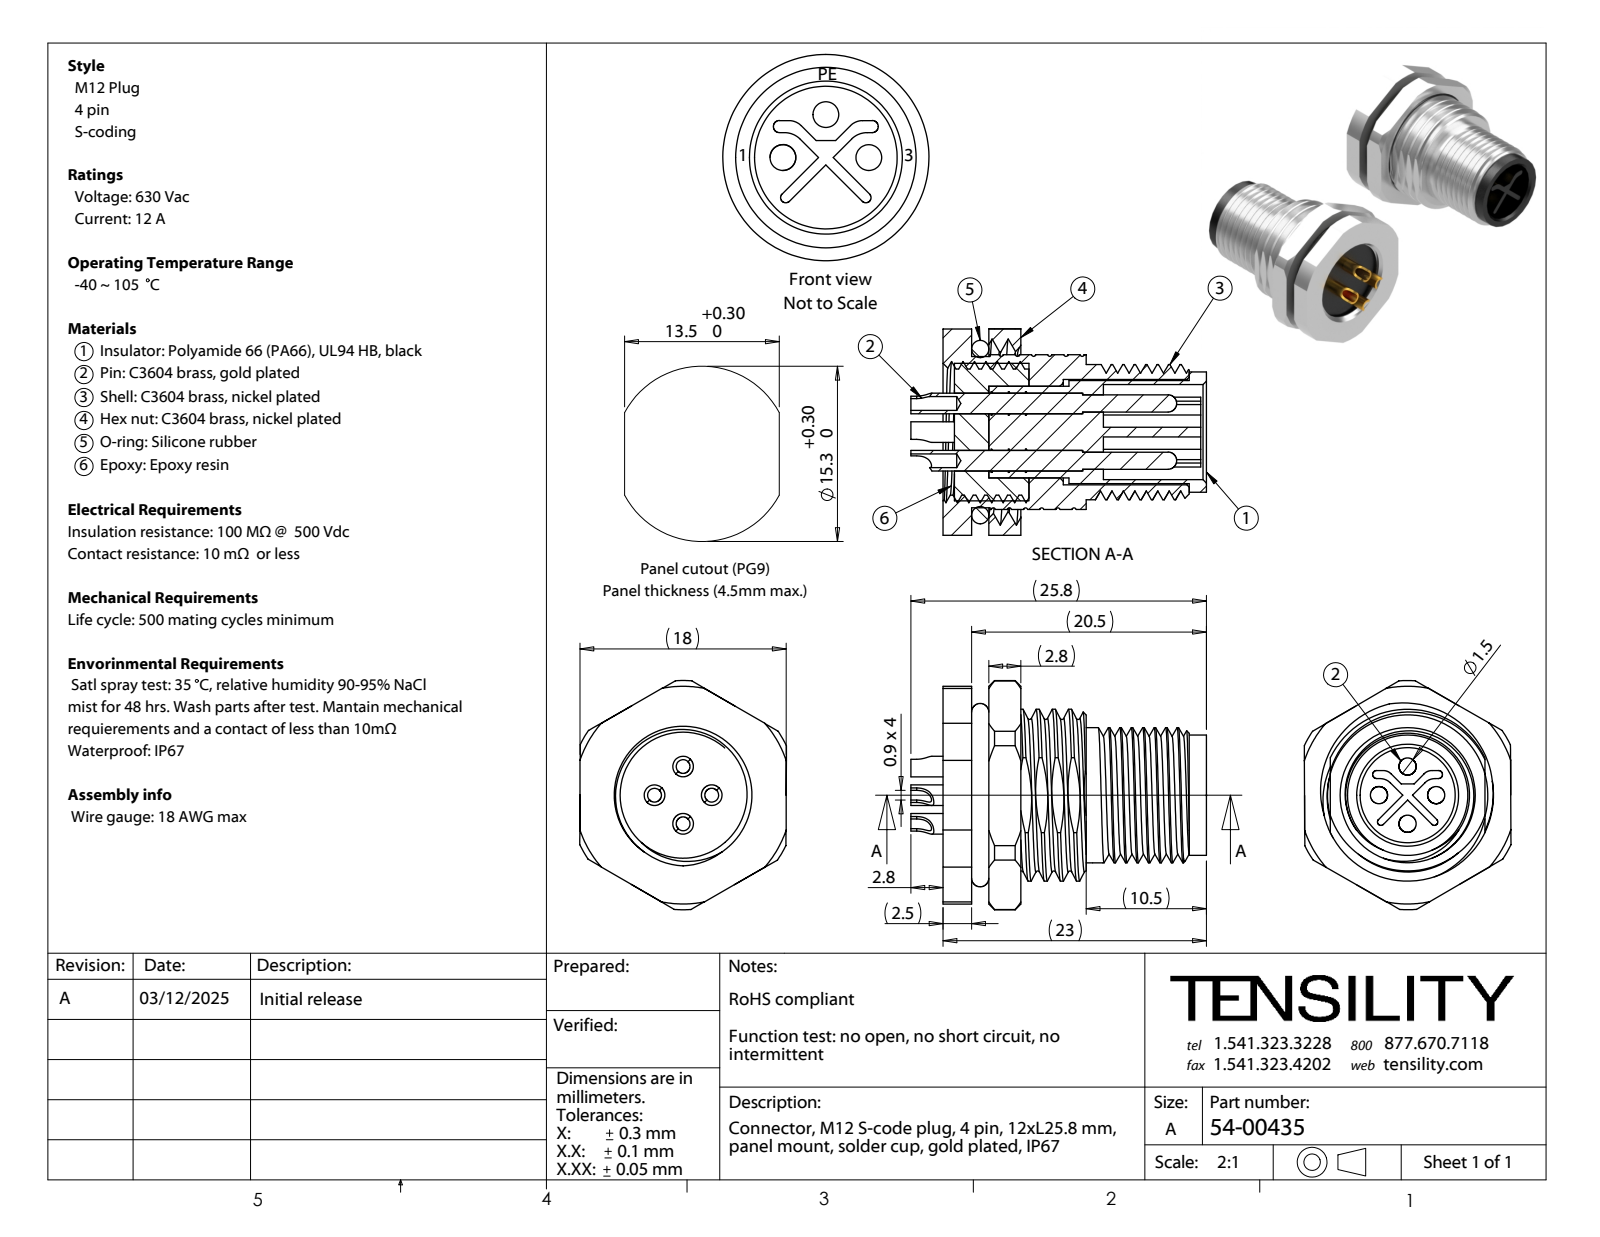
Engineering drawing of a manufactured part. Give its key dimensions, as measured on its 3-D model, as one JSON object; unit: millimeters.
{"part_name": "54-00435-03L; 54-00435-05; 54-00435-01; 54-00435-03 (+3 more)", "step_written_by": "SolidWorks 2021 (CONFIG_CONTROL_DESIGN)", "units": "millimeters", "bodies": {"solids": 9, "faces": 350, "planar": 92, "cylindrical": 162, "other": 96}, "overall_size": [25.8, 20, 18.04], "volume_mm3": 3131, "surface_area_mm2": 6017, "round_holes": [[1.2, 4], [1.5, 4], [8, 1], [8.3, 1], [9.2, 1], [11, 1], [14, 1]], "round_bosses_or_shafts": [[1.8, 4], [13.2, 1], [12, 1], [11.8, 1], [10.5, 1], [9, 1]], "partial_cylinders_radius": [[0.3, 2], [0.35, 2], [1, 2], [1.28, 2], [1.7, 2], [7.5, 1], [9.5, 1], [10, 1]], "face_to_face_distances": [1.5, 4, 5, 6.5, 7.5, 2.5, 3.5, 3, 1, 10], "hole_center_spacings": [2.5, 3.54, 5]}
